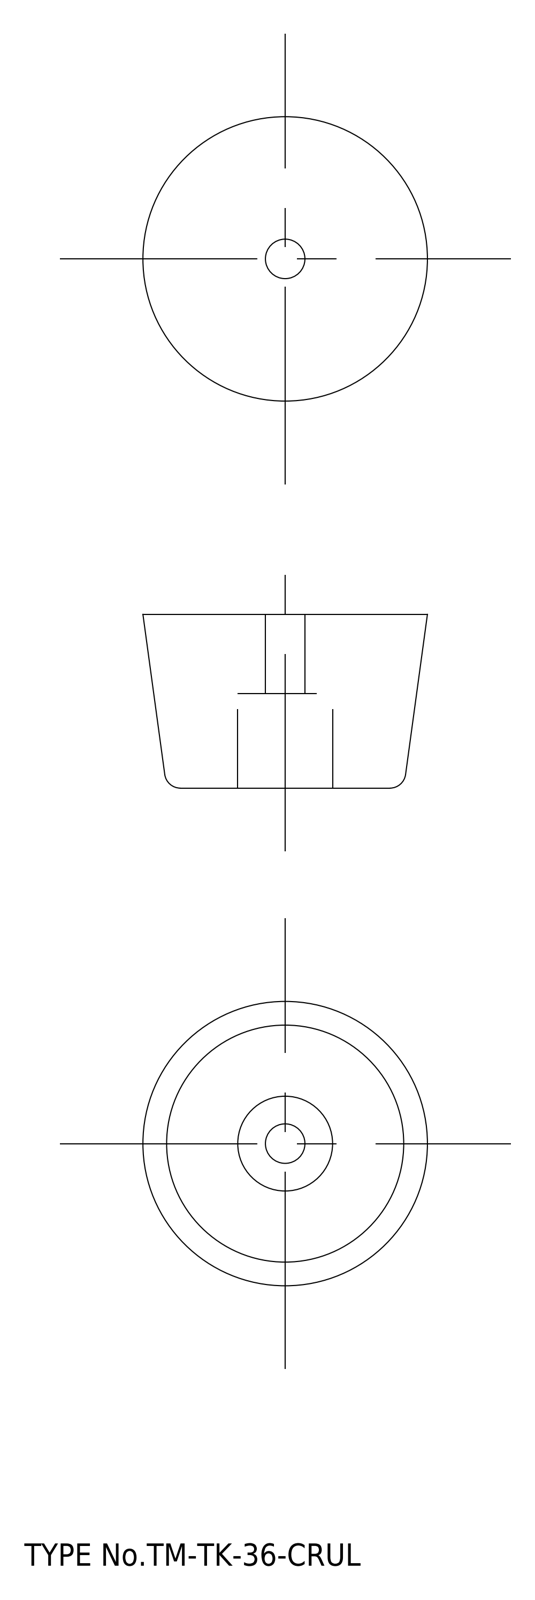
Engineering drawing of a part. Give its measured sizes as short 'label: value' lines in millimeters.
name: washer; rubber foot
written by: spGate 15.6.1 (AUTOMOTIVE_DESIGN)
unit: mm
bodies: 2 solids, 20 faces (6 planar, 10 cylindrical, 4 other)
size: 36 × 36 × 22
volume: 17 294 mm³; area: 5 159 mm²
holes: 1× ⌀5, 1× ⌀12, 1× ⌀16
face distances: 22, 12.8, 9.2, 12, 0.8, 10
